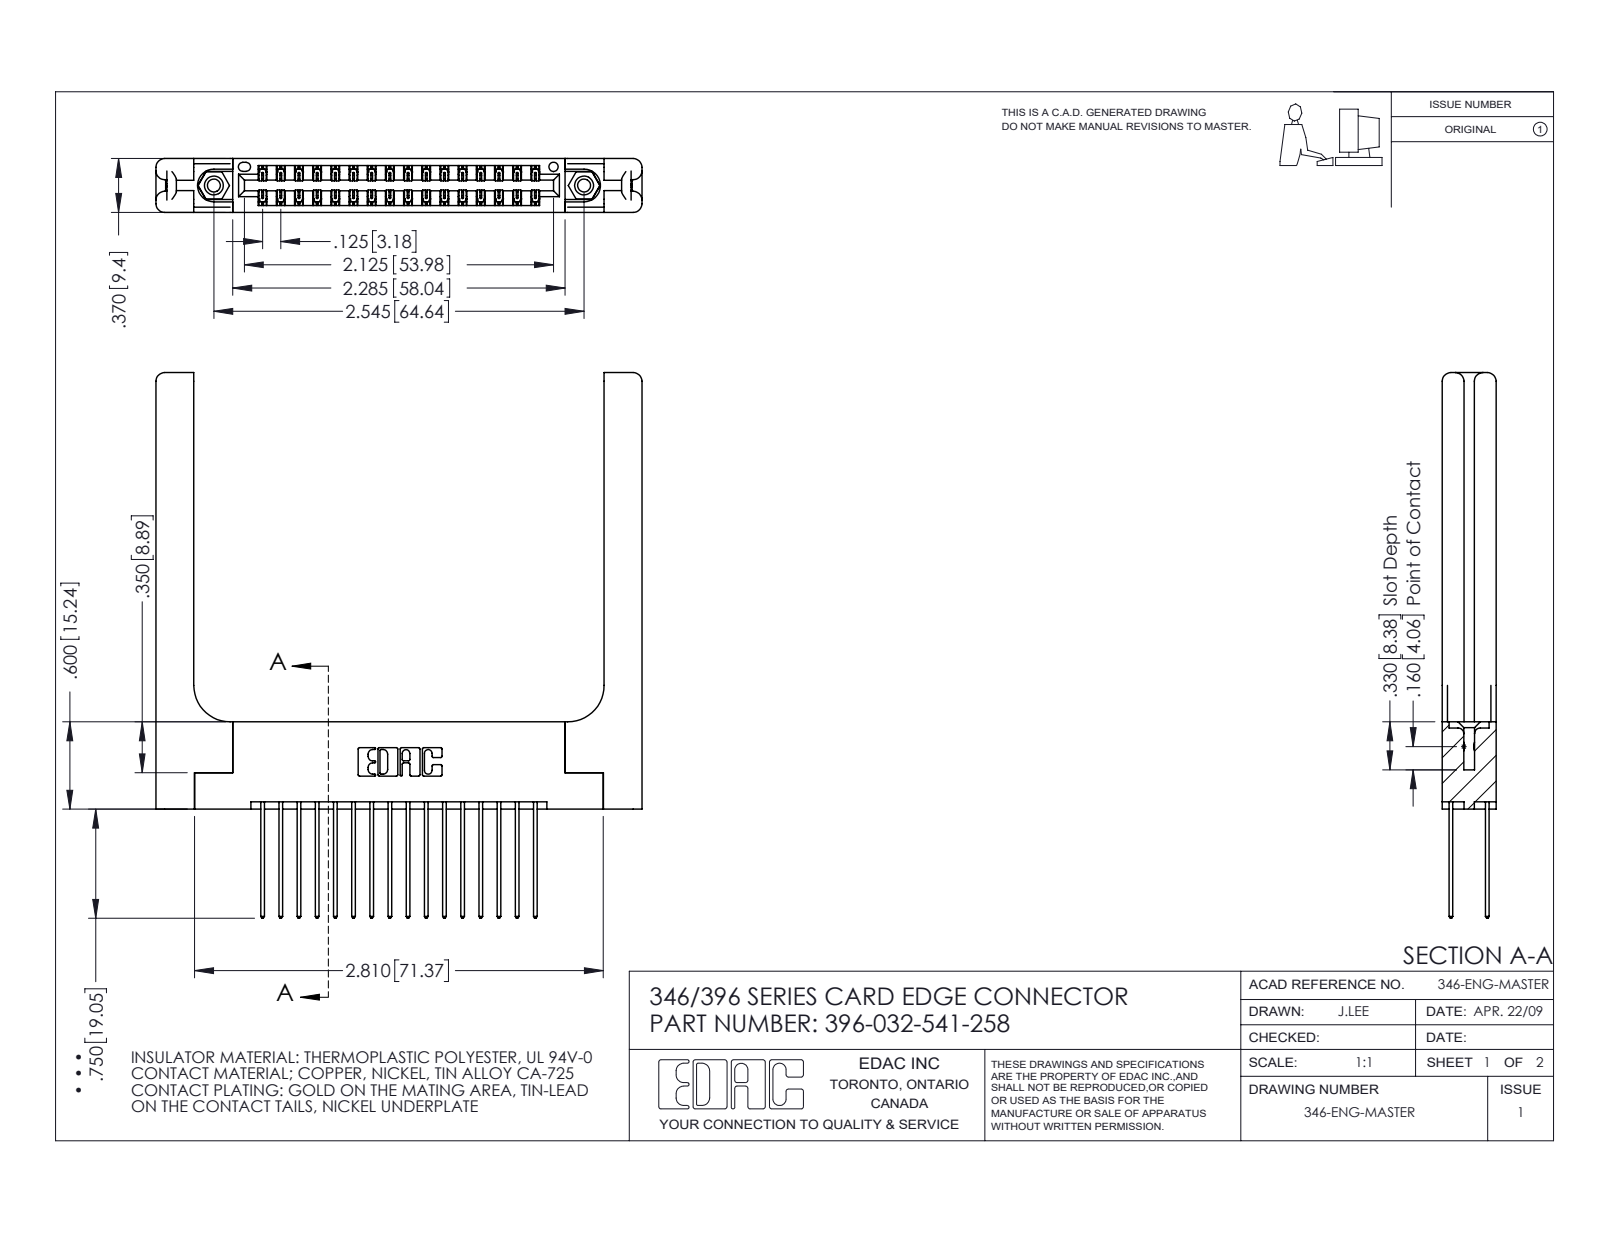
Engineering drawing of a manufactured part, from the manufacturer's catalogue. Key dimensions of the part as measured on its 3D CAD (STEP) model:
Part name (STEP PRODUCT): 346 Part_Flush Mounting Lugs - 0.156 Dia-TH; 346-220-058_345-220-058; 345-250-001_345-250-001-102; 345-292-001_345-293-141 (+1 more)
STEP written by: SolidWorks 2016 (CONFIG_CONTROL_DESIGN)
Units: inches
Bodies: 37 solids, 2042 faces (1344 planar, 638 cylindrical, 60 other)
Overall size (bounding box): 3.75 × 3.341 × 0.37
Volume: 0.961 in³ · Surface area: 26.03 in²
Round holes (diameter × count): ⌀0.089 ×2, ⌀0.125 ×2, ⌀0.156 ×2, ⌀0.064 ×1
Round bosses / shafts (diameter × count): ⌀0.155 ×2
Partial cylindrical surfaces — rounded edges, fillets, slot ends (radius × count): R0.006 ×48, R0.01 ×32, R0.01 ×22, R0.06 ×16, R0.007 ×6, R0.031 ×6, R0.026 ×3, R0.014 ×2
Main face-to-face distances: 0.37, 0.072, 0.048, 0.322, 0.25, 0.148, 0.15, 0.025, 0.298, 0.077
Hole centre spacings: 0.246, 2.338, 2.545
